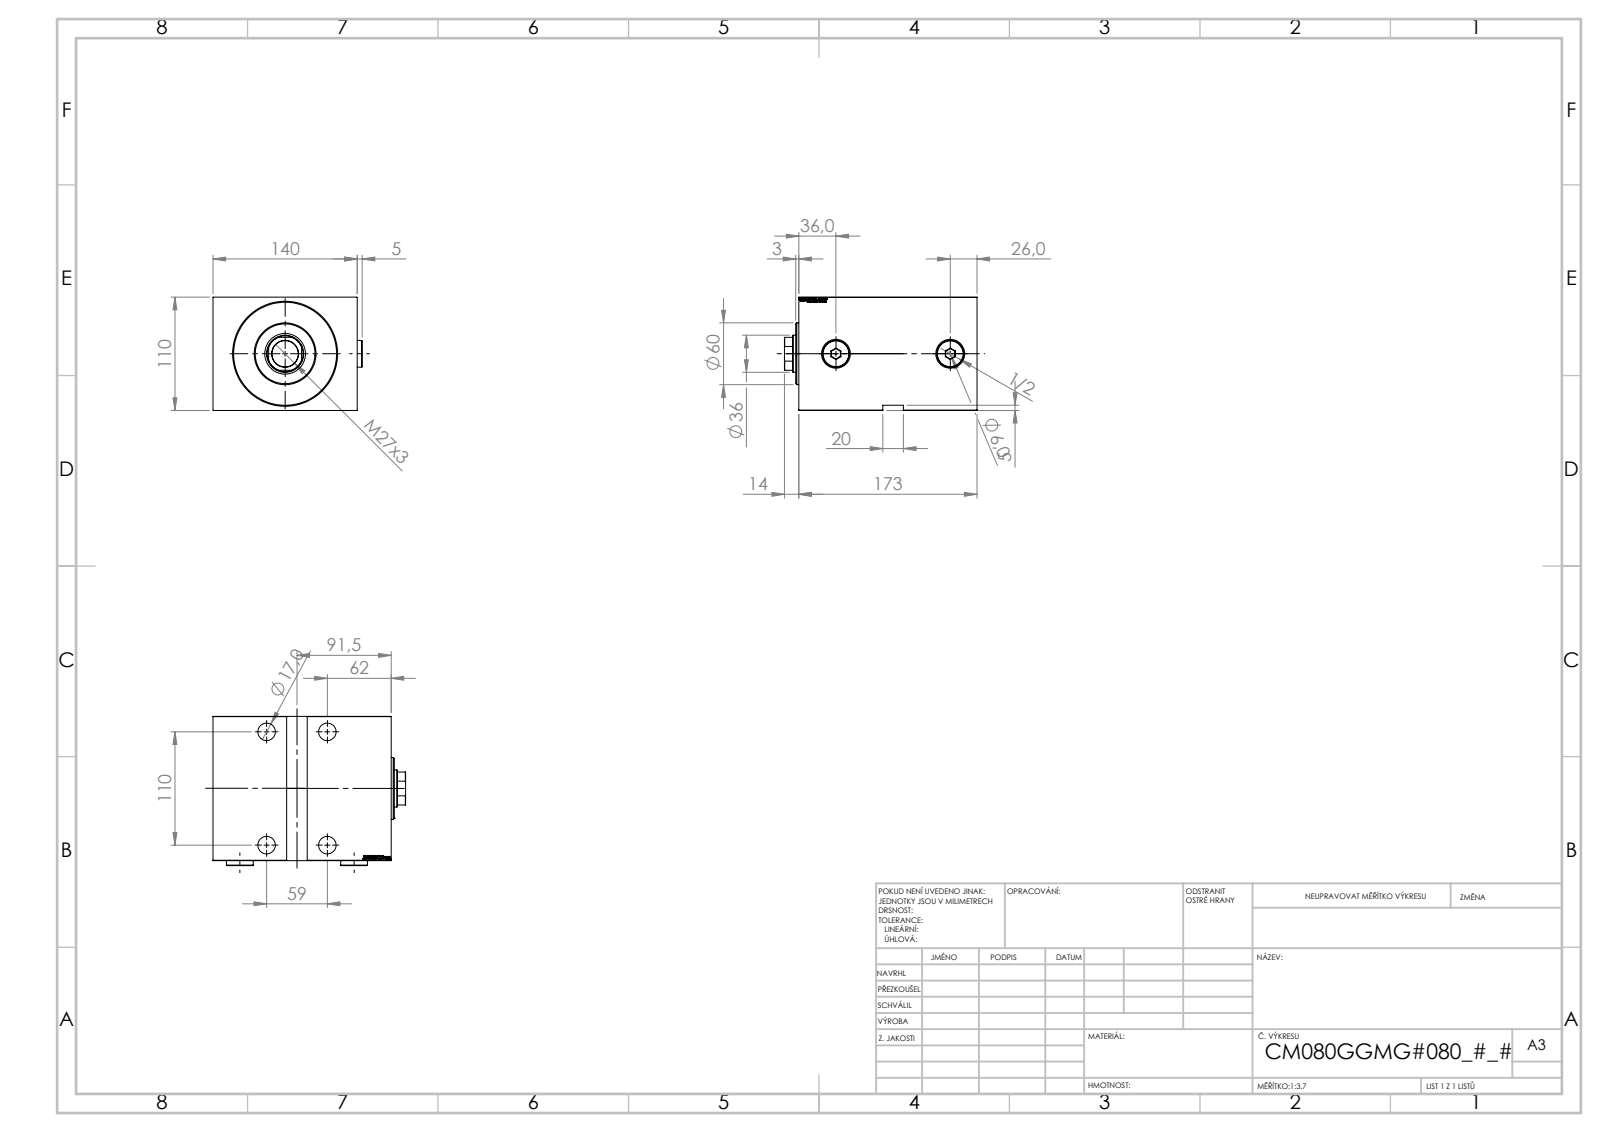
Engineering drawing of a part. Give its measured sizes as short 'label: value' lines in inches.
name: V450CM_VC_G; V450CM_G_Body; Zatka_OIL_PORT; V450CM_G_VCP
written by: SolidWorks 2019 (CONFIG_CONTROL_DESIGN)
unit: in
bodies: 5 solids, 896 faces (442 planar, 56 cylindrical, 398 other)
size: 7.362 × 5.705 × 4.331
volume: 131.8 in³; area: 375.6 in²
holes: 4× ⌀0.669, 4× ⌀0.984, 2× ⌀0.236, 2× ⌀0.825, 2× ⌀1.102, 1× ⌀1.004, 1× ⌀1.417, 1× ⌀1.555, 1× ⌀3.15, 1× ⌀3.228, 1× ⌀3.937
bosses: 2× ⌀1.024, 1× ⌀2.362
rounds: 1× R0.689
face distances: 4.331, 5.512, 0.197, 6.811, 0.827, 5.984, 6.614, 5.787, 3.11, 2.283
hole spacings: 2.323, 4.331, 4.914, 4.37
